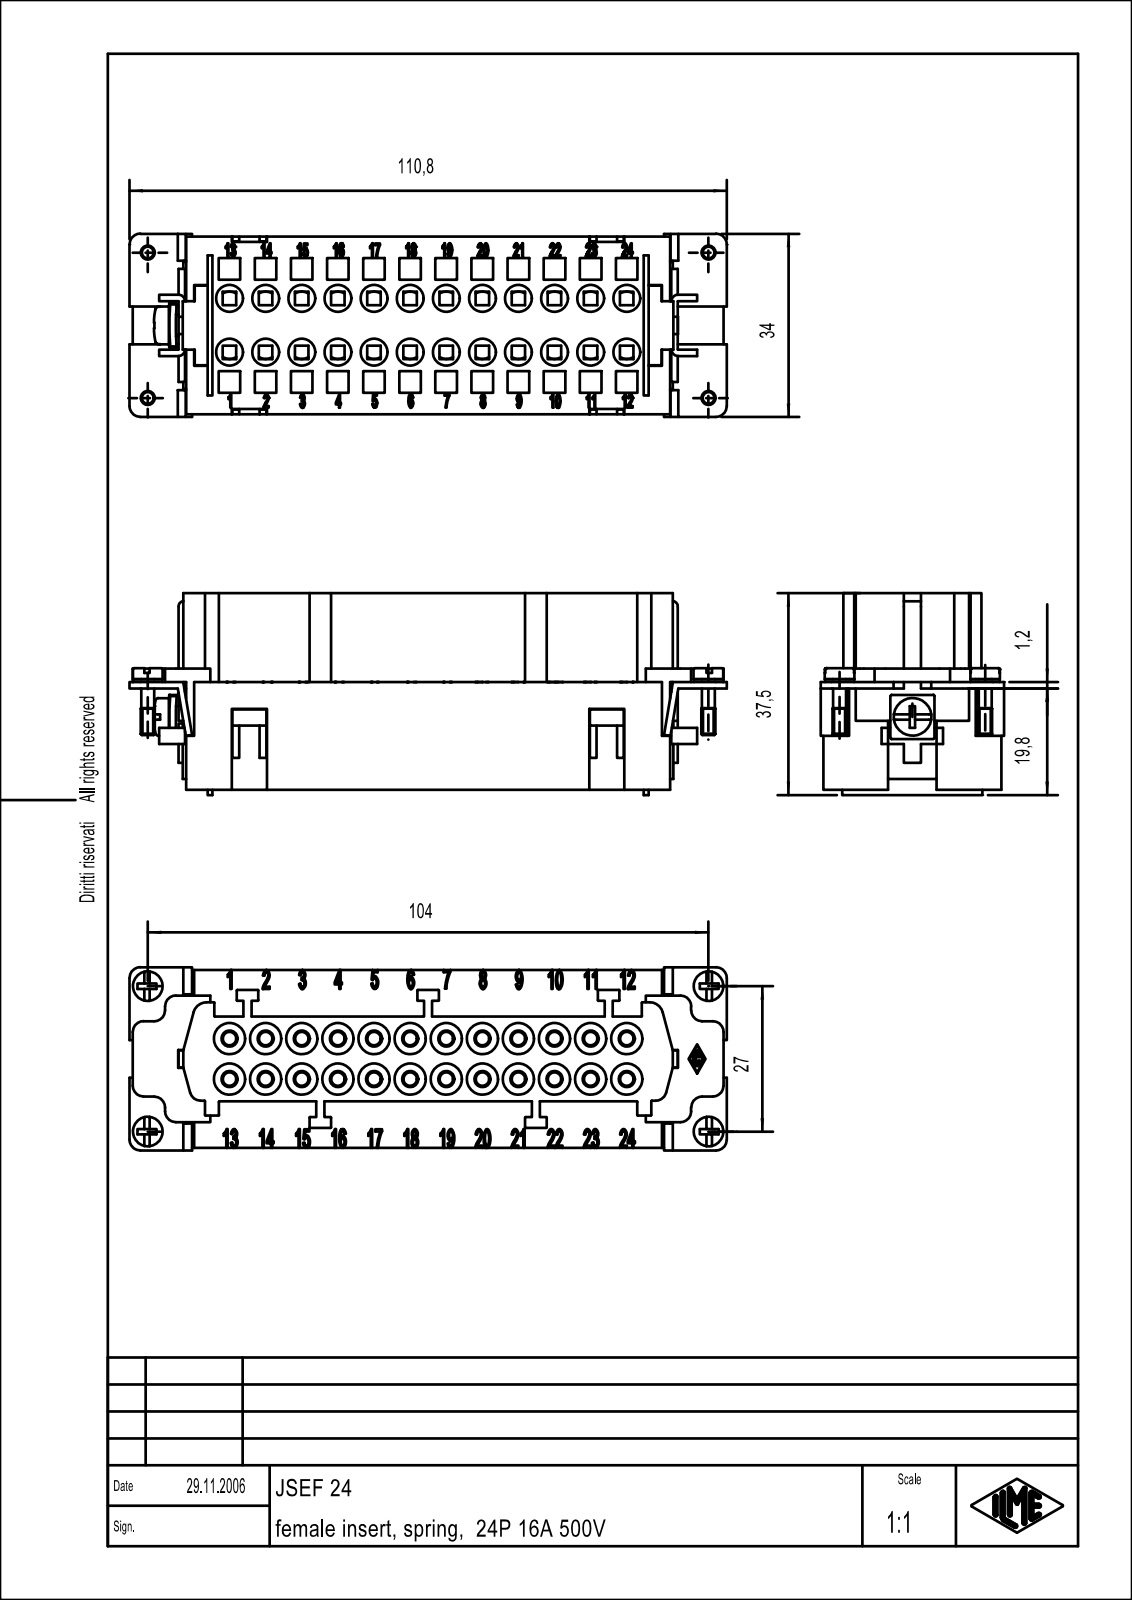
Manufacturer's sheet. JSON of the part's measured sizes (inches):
{"part_name": "CSEF_Kontakteins\\S\\dtze_mit_K\\S\\dfigzugfederanschluss; JSEF_24.stp", "step_written_by": "Creo Elements/Direct Modeling 18.0B 02-Dec-2011 (C) Parametric Technology GmbH (AUTOMOTIVE_DESIGN)", "units": "inches", "bodies": {"solids": 1, "faces": 2253, "planar": 1239, "cylindrical": 390, "other": 624}, "overall_size": [4.362, 1.476, 1.339], "volume_in3": 4.61, "surface_area_in2": 49.64, "round_holes": [[0.197, 48], [0.098, 24], [0.118, 24], [0.228, 24], [0.128, 1]], "round_bosses_or_shafts": [[0.217, 4], [0.213, 4], [0.102, 4], [0.094, 4], [0.276, 1], [0.157, 1]], "partial_cylinders_radius": [[0.004, 32], [0.079, 18], [0.004, 14], [0.049, 4], [0.039, 2], [0.098, 2], [0.223, 1]], "face_to_face_distances": [0.157, 0.339, 0.96, 0.787, 0.394, 1.299, 0.984, 0.62, 0.315, 0.492], "hole_center_spacings": [0.264, 0.528, 0.474, 0.658, 0.791, 0.884, 1.055, 1.126]}
